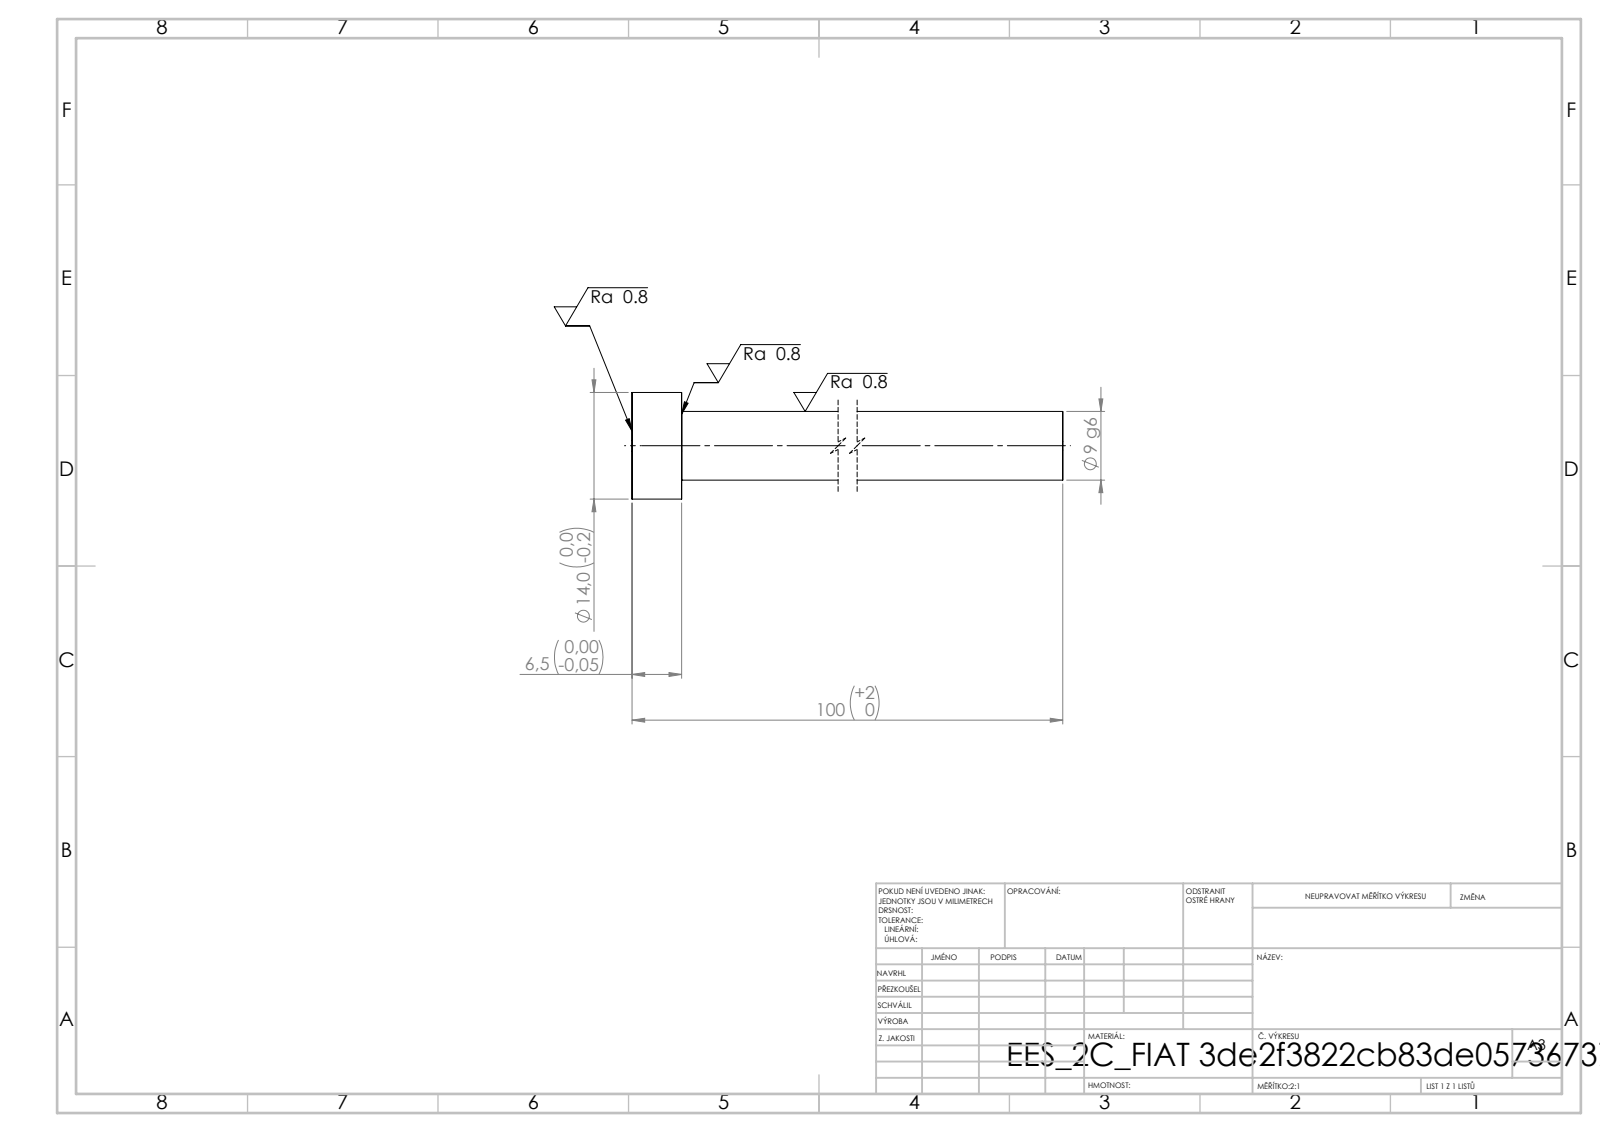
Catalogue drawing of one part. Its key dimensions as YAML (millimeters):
step_written_by: "SolidWorks 2019 (CONFIG_CONTROL_DESIGN)"
units: millimeters
bodies: {solids: 1, faces: 7, planar: 3, cylindrical: 4, other: 0}
overall_size: [100, 14, 14]
volume: 6949
surface_area: 3237
round_bosses_or_shafts:
  - {diameter: 14, count: 1}
  - {diameter: 9, count: 1}
face_to_face_distances: [6.5, 100, 93.5]
